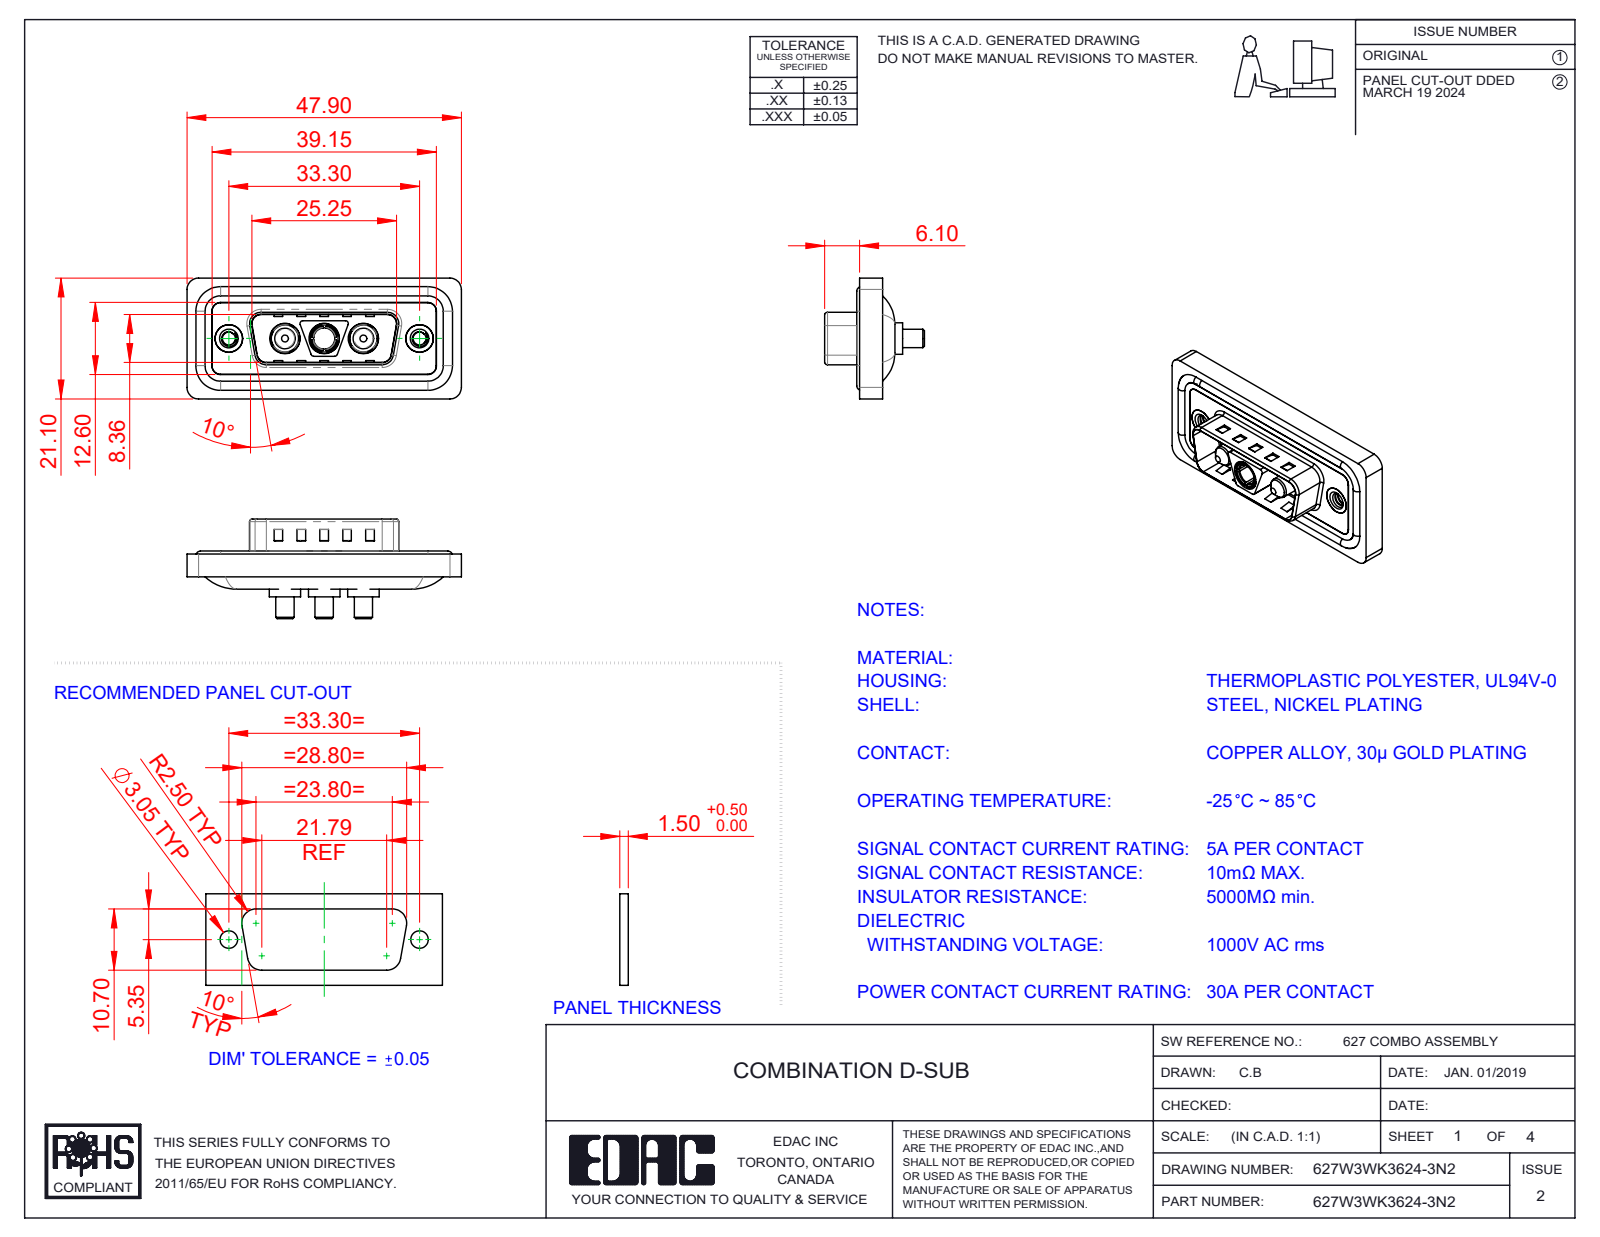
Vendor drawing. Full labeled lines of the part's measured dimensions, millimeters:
Part name (STEP PRODUCT): 627Combo Shell Front_15 Contacts; Power Pin_30A S; Power Socket_30A S; 627Combo Threaded Rivet_2 (+4 more)
STEP written by: SolidWorks 2023 (CONFIG_CONTROL_DESIGN)
Units: millimetres
Bodies: 13 solids, 609 faces (231 planar, 250 cylindrical, 128 other)
Overall size (bounding box): 47.9 × 21.1 × 17.4
Volume: 5 709 mm³ · Surface area: 9 141 mm²
Round holes (diameter × count): ⌀4.85 ×3, ⌀5.3 ×3, ⌀2.26 ×2, ⌀4 ×2, ⌀4.8 ×2, ⌀5 ×2, ⌀3.7 ×1
Round bosses / shafts (diameter × count): ⌀1.6 ×4, ⌀5.5 ×3, ⌀5.2 ×3, ⌀4.75 ×3, ⌀3.75 ×3, ⌀3.2 ×3, ⌀4.9 ×2, ⌀3.6 ×2
Partial cylindrical surfaces — rounded edges, fillets, slot ends (radius × count): R1.5 ×26, R2 ×20, R0.5 ×12, R1.6 ×8, R0.25 ×4, R0.6 ×4, R0.65 ×4, R0.9 ×4
Main face-to-face distances: 0.4, 1.1, 1.5, 0.5, 1.6, 3.1, 2.9, 4, 0.82, 9.58
Hole centre spacings: 6.85, 9.8, 16.65, 23.5, 13.7, 33.3
